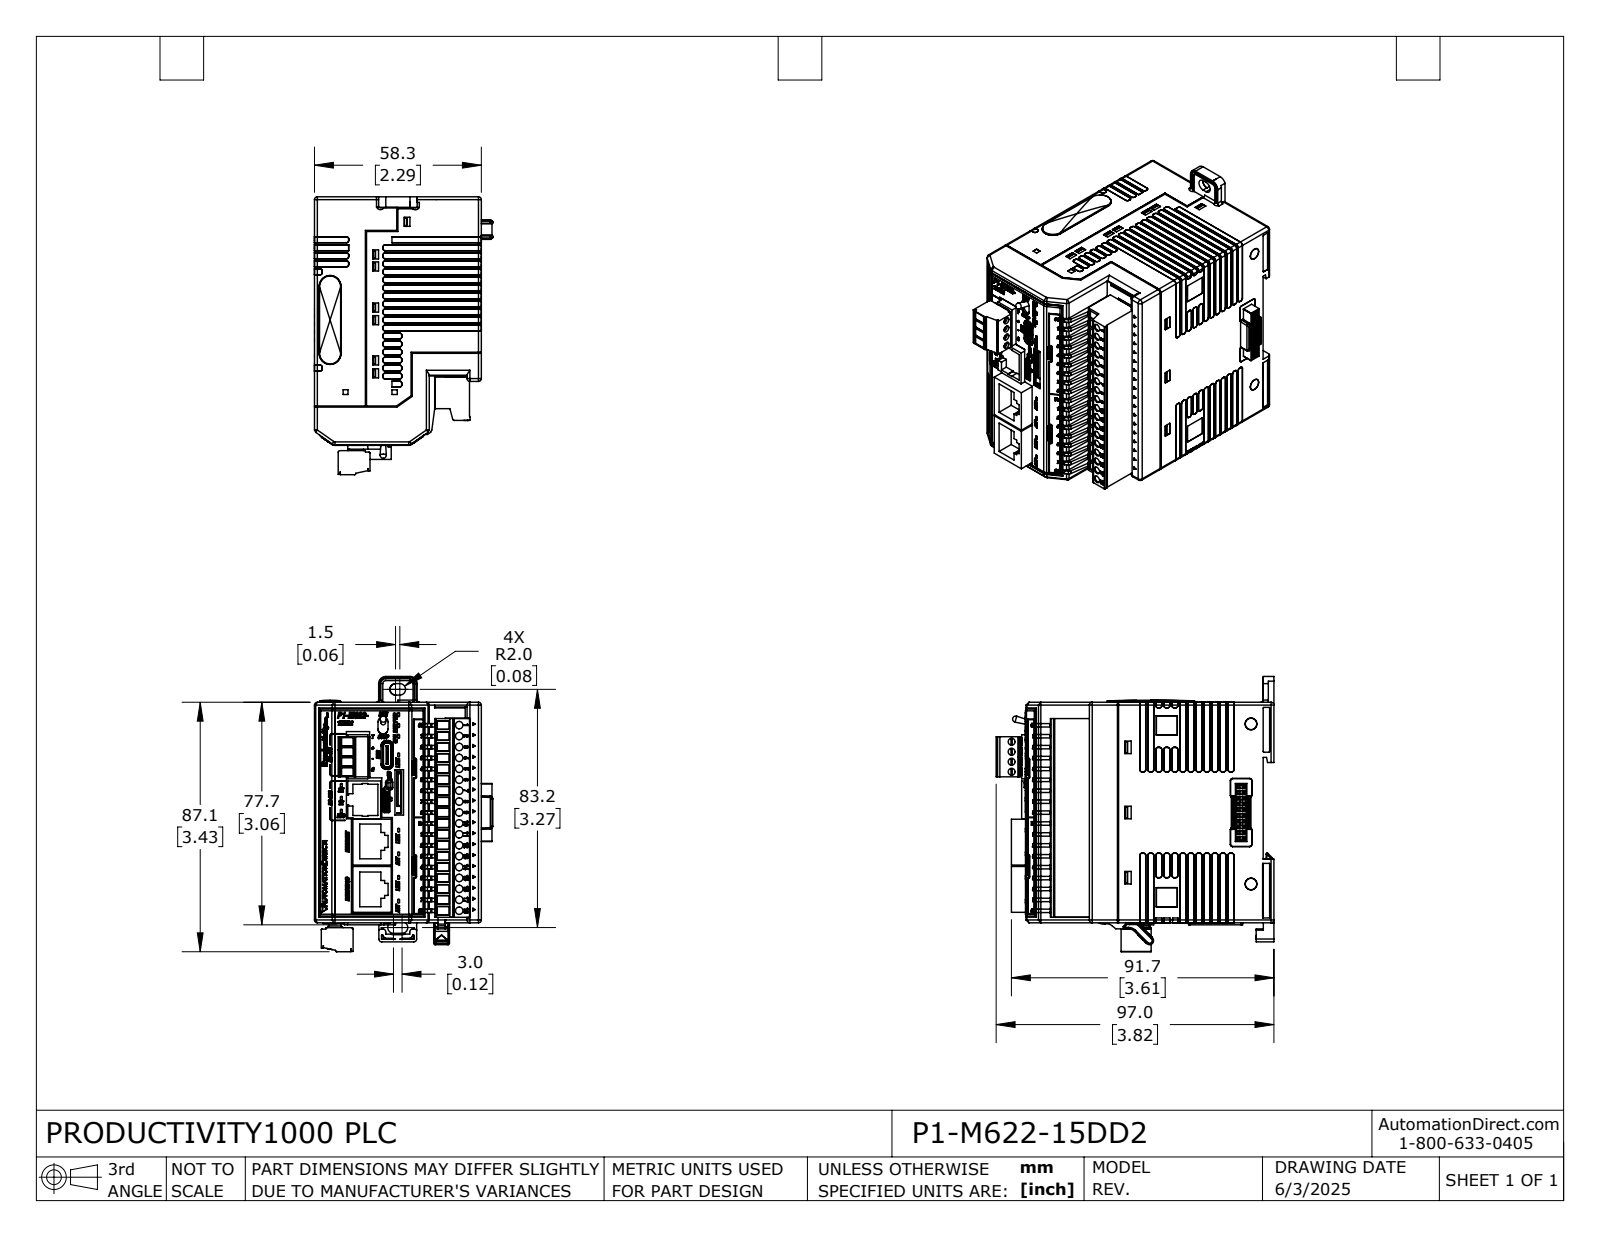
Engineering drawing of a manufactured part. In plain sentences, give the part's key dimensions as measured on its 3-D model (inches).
The part is named "P1-M622-15DD2". Its 3-D file was written by "SolidWorks 2024 (AUTOMOTIVE_DESIGN)". It is 12 solids with 3752 faces: 2141 planar, 886 cylindrical and 725 other. Overall it measures 3.686 by 3.61 by 2.452 inches. Its volume is 2.158 cubic inches and its surface area 118.3 square inches. Partial cylindrical surfaces (rounded edges, fillets, slot ends): 186 of radius 0.01, 80 of radius 0.008, 53 of radius 0.02, 33 of radius 0.039, 8 of radius 0.079, 7 of radius 0.024, 7 of radius 0.059, 4 of radius 0.012. The main face-to-face distances are 0.05, 0.02, 2.235, 0.039, 2.275, 3.01, 3.022, 2.294, 3.02, 3.031.
